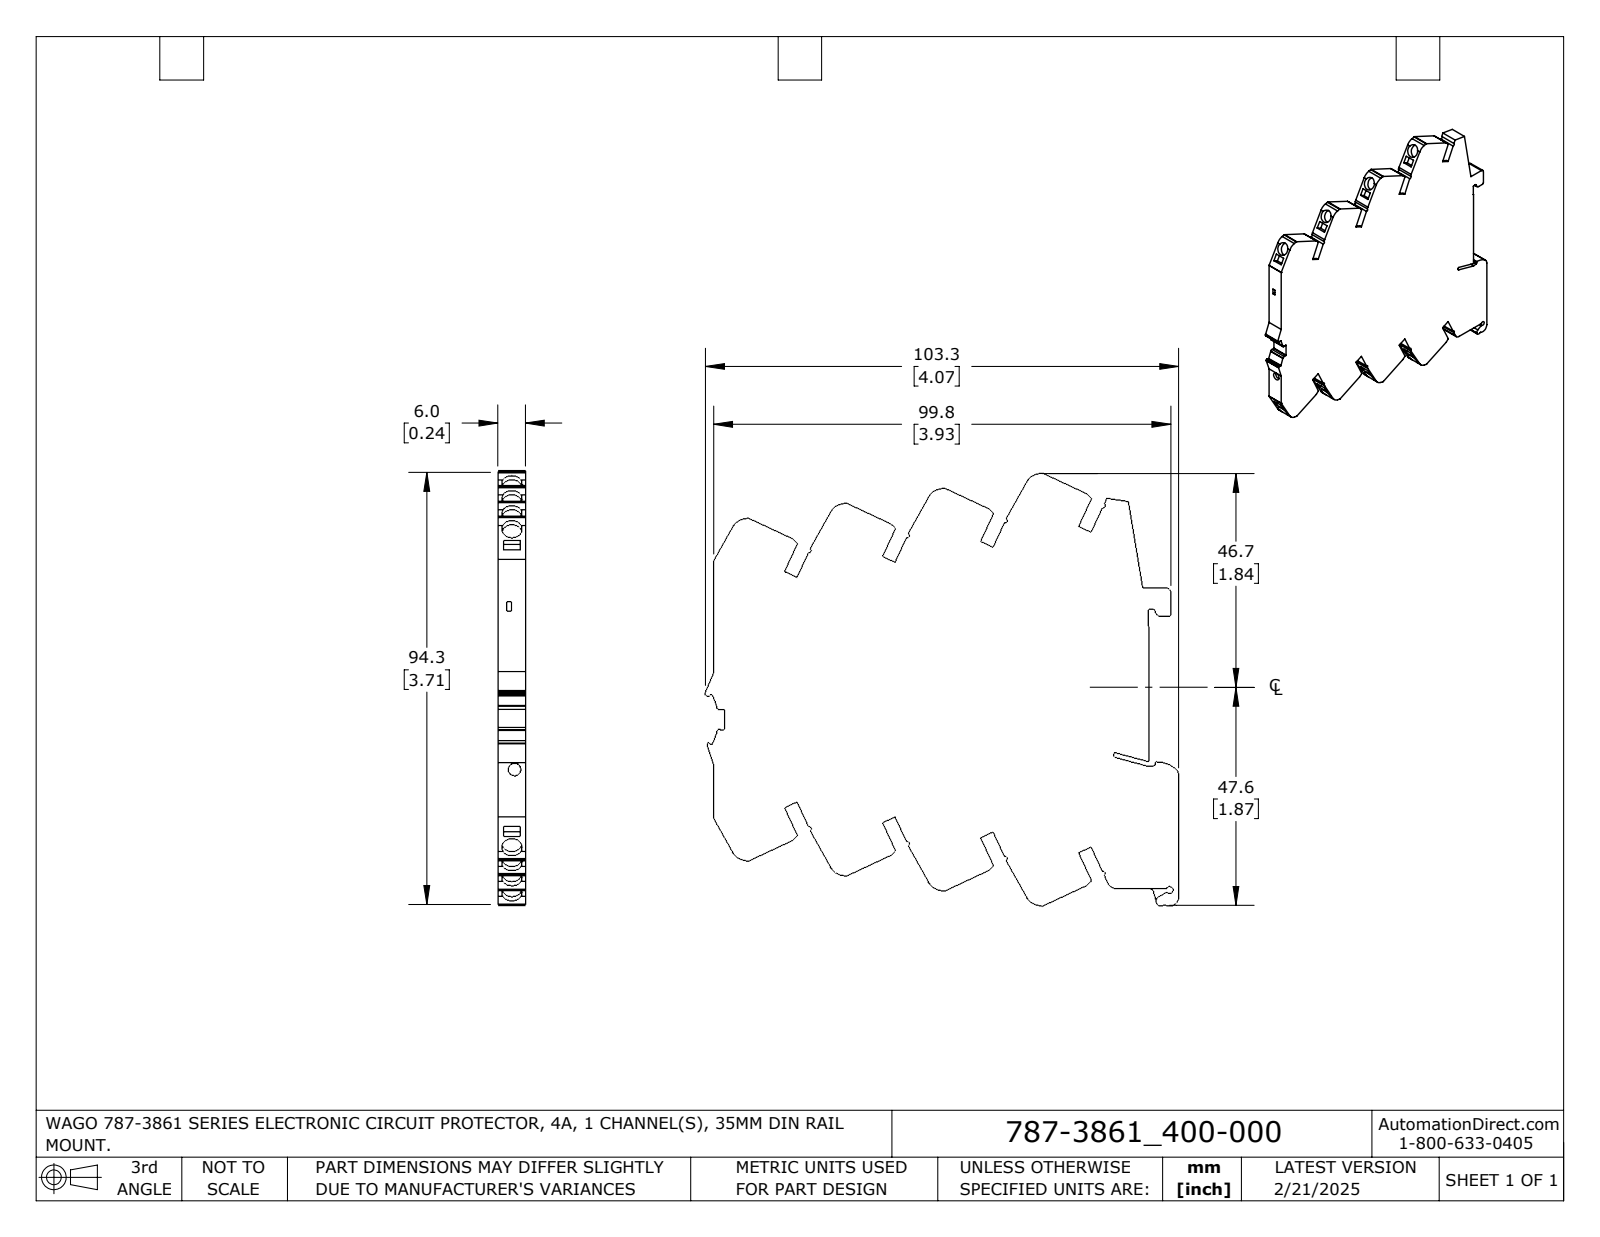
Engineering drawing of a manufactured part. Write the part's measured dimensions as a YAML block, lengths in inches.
part_name: "787-3861_400-000_HI"
step_written_by: "SolidWorks 2024 (AUTOMOTIVE_DESIGN)"
units: inches
bodies: {solids: 1, faces: 262, planar: 197, cylindrical: 65, other: 0}
overall_size: [4.067, 3.711, 0.236]
volume: 2.685
surface_area: 29.24
round_holes:
  - {diameter: 0.173, count: 8}
  - {diameter: 0.106, count: 1}
partial_cylinders:
  - {radius: 0.008, count: 13}
  - {radius: 0.02, count: 12}
  - {radius: 0.016, count: 8}
  - {radius: 0.132, count: 8}
  - {radius: 0.039, count: 5}
  - {radius: 0.012, count: 3}
  - {radius: 0.079, count: 3}
  - {radius: 0.018, count: 2}
face_to_face_distances: [0.236, 0.708, 1.417, 0.118, 0.473, 0.826, 0.67, 0.472, 0.945, 1.535]
hole_center_spacings: [0.526, 1.052, 1.577]
